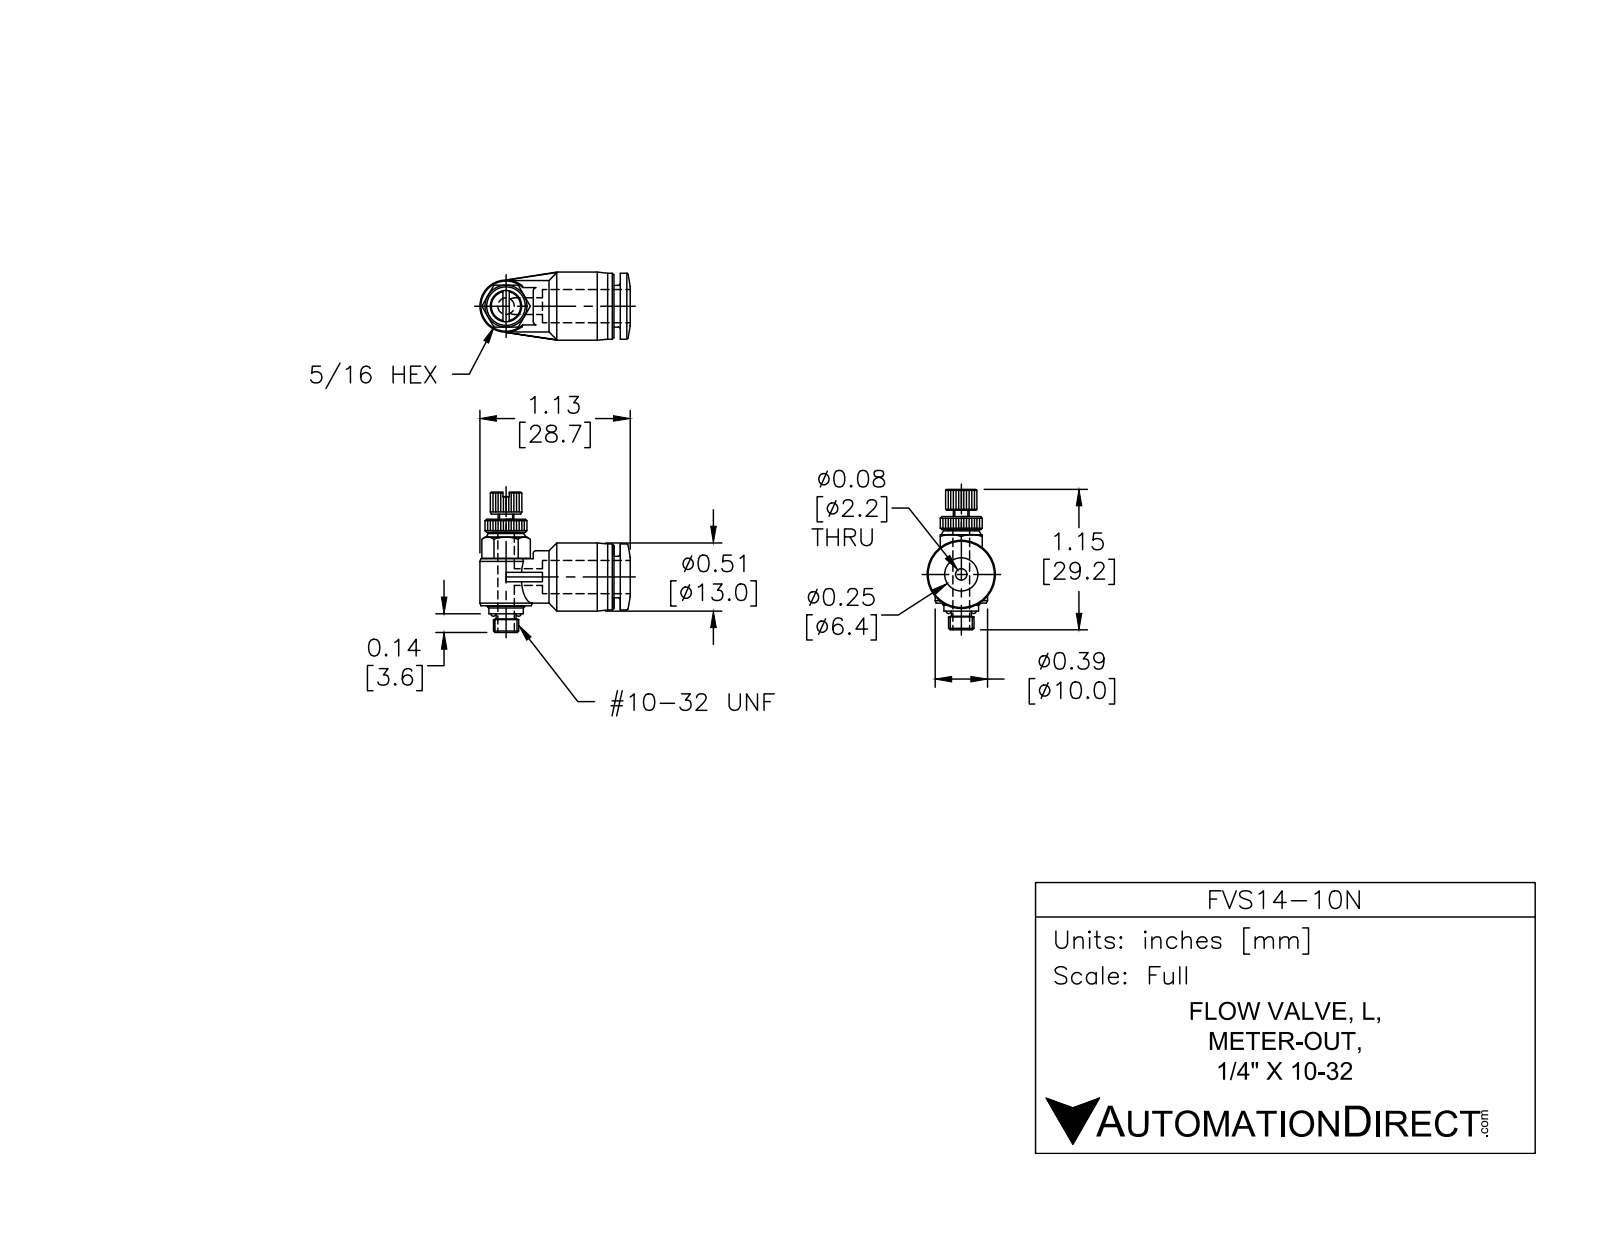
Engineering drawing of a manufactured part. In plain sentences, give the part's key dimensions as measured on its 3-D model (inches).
The part is named "FVS14-10N". Its 3-D file was written by "SolidWorks 2015 (AUTOMOTIVE_DESIGN)". It is 2 solids with 351 faces: 147 planar, 99 cylindrical and 105 other. Overall it measures 1.146 by 1.13 by 0.512 inches. Its volume is 0.178 cubic inches and its surface area 3.724 square inches. Round holes: 2 of diameter 0.059, 1 of diameter 0.15, 1 of diameter 0.258. Round bosses or shafts: 2 of diameter 0.394, 1 of diameter 0.512, 1 of diameter 0.496, 1 of diameter 0.313, 1 of diameter 0.299, 1 of diameter 0.28, 1 of diameter 0.264, 1 of diameter 0.26. Partial cylindrical surfaces (rounded edges, fillets, slot ends): 1 of radius 0.118, 1 of radius 0.157. The main face-to-face distances are 0.047, 0.315, 0.297, 0.587, 0.098, 0.652, 0.354, 0.539, 0.206, 0.293.
